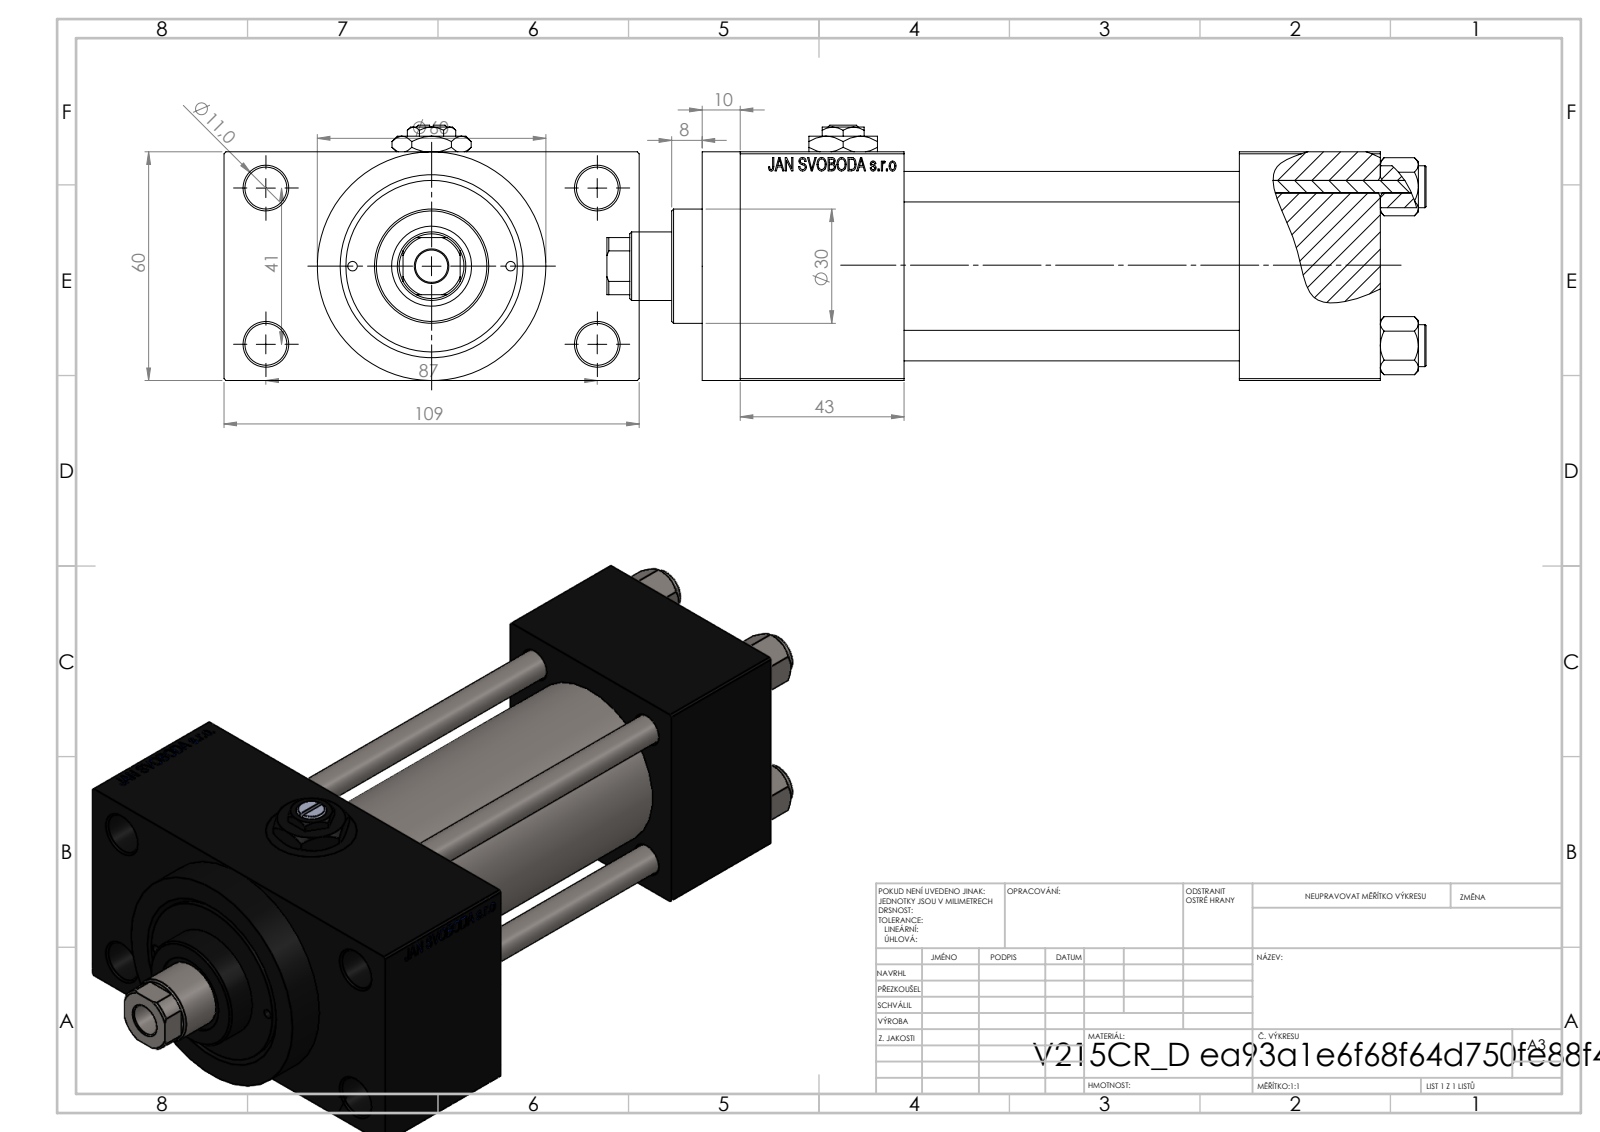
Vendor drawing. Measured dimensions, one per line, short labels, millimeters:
name: Zatka_pro_OIL_PORT; V215CR_VCP_D; V215CR_D_TYCINKA; V215CR_D_Body (+2 more)
written by: SolidWorks 2019 (CONFIG_CONTROL_DESIGN)
unit: mm
bodies: 12 solids, 1160 faces (524 planar, 96 cylindrical, 540 other)
size: 215 × 109 × 67
volume: 537 701 mm³; area: 136 233 mm²
holes: 4× ⌀8, 4× ⌀11, 3× ⌀16.66, 3× ⌀24, 2× ⌀2.5, 2× ⌀7, 1× ⌀8.5, 1× ⌀18, 1× ⌀21, 1× ⌀31, 1× ⌀40, 1× ⌀45
bosses: 4× ⌀11, 1× ⌀60, 1× ⌀46, 1× ⌀30
rounds: 1× R8.5
face distances: 60, 88, 24.5, 84.5, 37, 125, 43, 168, 131, 10
hole spacings: 20.85, 22.65, 29.49, 30.62, 41.7, 46.53, 47.15, 48.09
